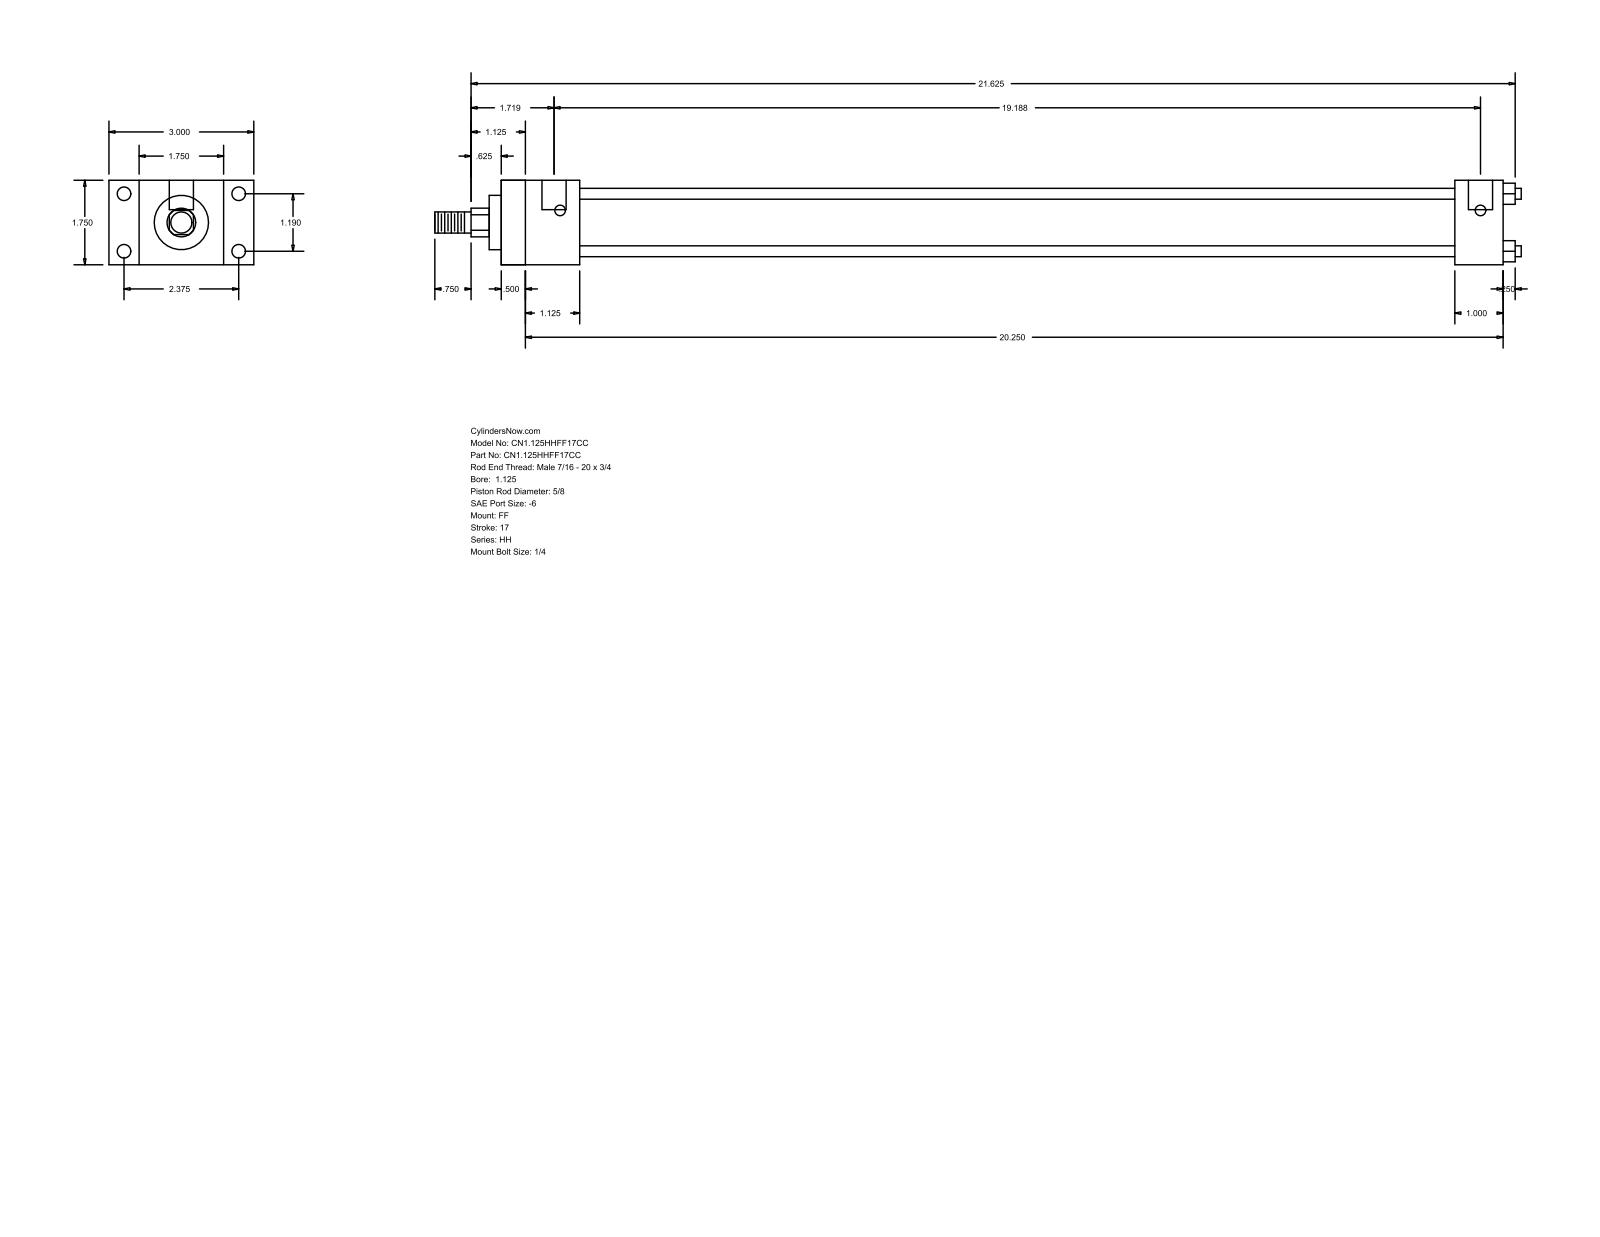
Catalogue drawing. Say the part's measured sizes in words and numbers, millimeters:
The part is named "HH_FF__0112_0.625". Its 3-D file was written by "GSSL Pune (CONFIG_CONTROL_DESIGN)". It is 0 solids with 92 faces: 64 planar, 28 cylindrical and 0 other. Overall it measures 571.5 by 76.2 by 44.45 millimeters. Round holes: 4 of diameter 5.56, 4 of diameter 7.14, 2 of diameter 12.7. Round bosses or shafts: 4 of diameter 5.71, 1 of diameter 34.92, 1 of diameter 28.57, 1 of diameter 15.88, 1 of diameter 11.11. Partial cylindrical surfaces (rounded edges, fillets, slot ends): 1 of radius 7.54. The main face-to-face distances are 44.46, 527.04, 12.69, 514.35, 15.87, 28.58, 60.33, 25.4, 41.27, 501.64. The hole center spacings are 30.22, 60.32, 67.47, 484.19, 3.17, 487.36.
